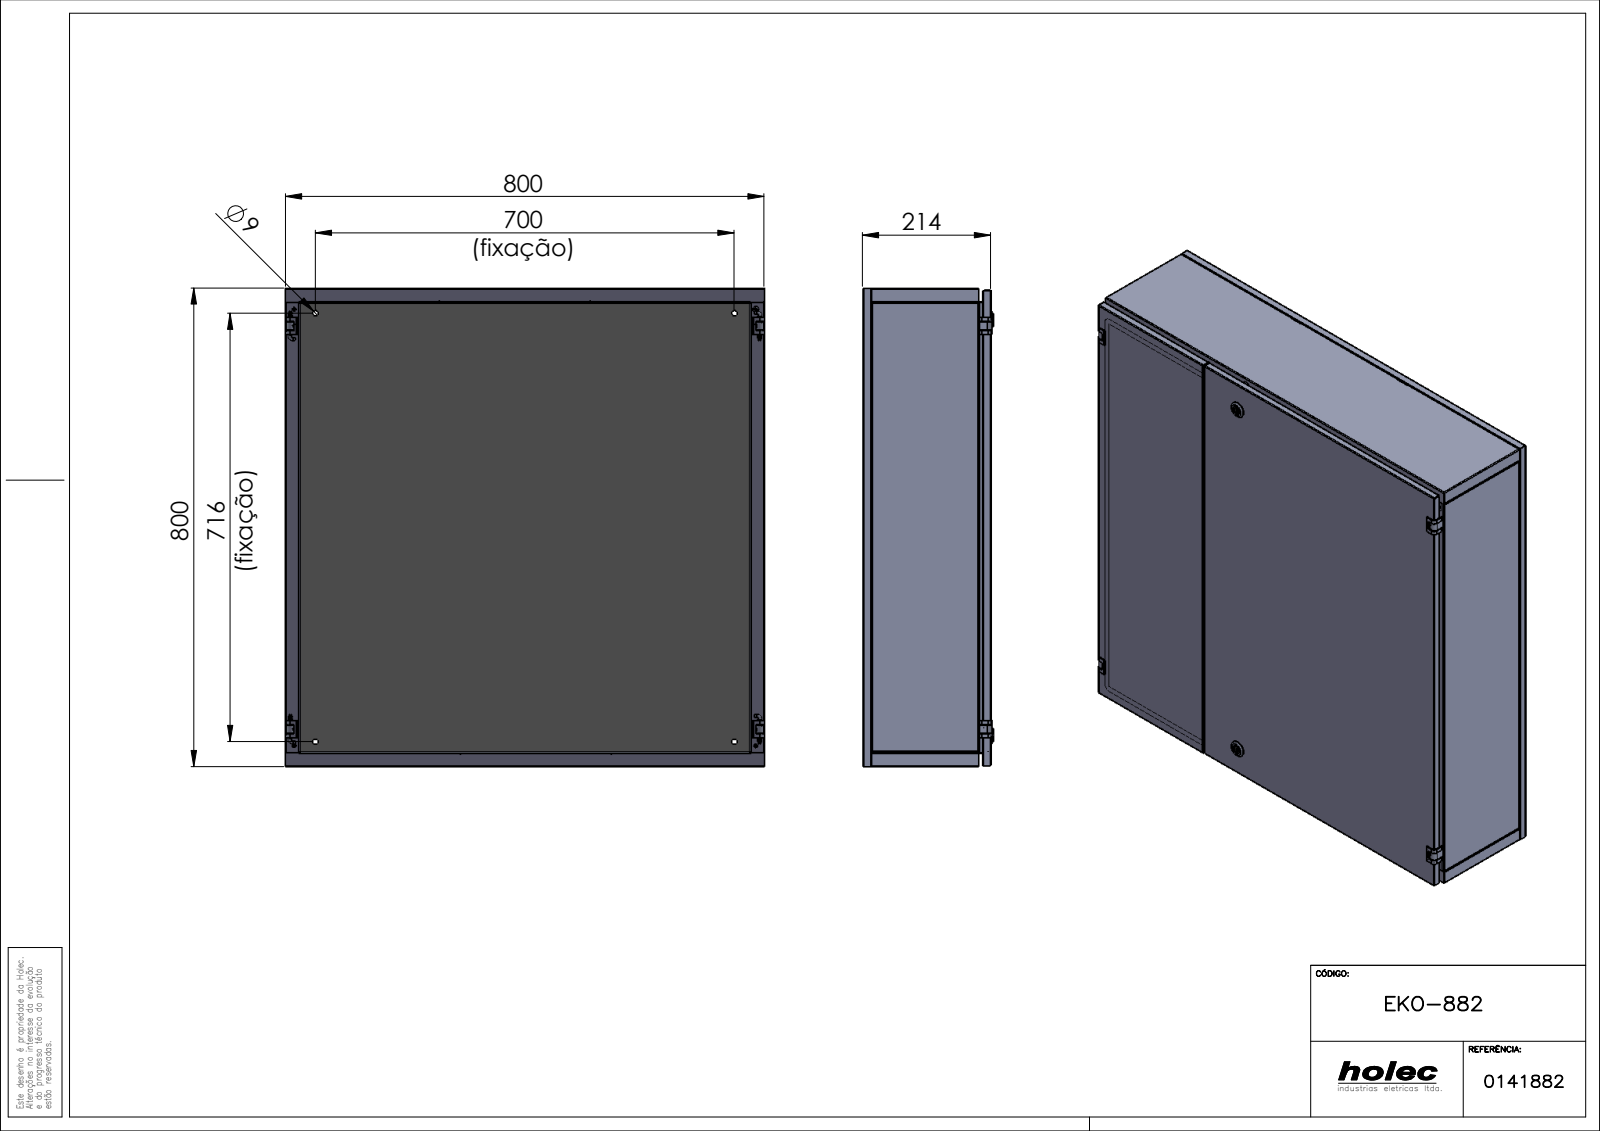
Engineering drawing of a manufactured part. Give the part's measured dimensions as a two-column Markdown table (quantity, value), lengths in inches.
| quantity | value |
| --- | --- |
| part name | EKO-882 |
| STEP written by | SolidWorks 2017 (AUTOMOTIVE_DESIGN) |
| units | inches |
| bodies | 53 solids, 3633 faces (1785 planar, 1142 cylindrical, 706 other) |
| overall size | 31.496 × 31.496 × 8.587 |
| volume | 153.6 in³ |
| surface area | 7 572 in² |
| round holes (diameter × count) | 0.169 × 36, 0.236 × 14, 0.165 × 12, 0.217 × 8, 0.433 × 8, 0.197 × 6, 0.13 × 4, 0.157 × 4, 0.354 × 4, 0.161 × 2, 0.394 × 2, 0.398 × 2 |
| round bosses / shafts (diameter × count) | 0.157 × 4, 1.102 × 2, 0.748 × 2, 0.618 × 2, 0.591 × 2, 0.5 × 2, 0.374 × 2, 0.23 × 2 |
| partial cylindrical surfaces (radius × count) | 0.008 × 152, 0.059 × 59, 0.02 × 57, 0.012 × 40, 0.039 × 22, 0.098 × 14, 0.079 × 8, 0.177 × 6 |
| main face-to-face distances | 0.039, 8.39, 8.35, 8.429, 31.457, 31.417, 31.496, 0.945, 30.512, 0.902 |
| hole center spacings | 0.984, 1.236, 9.97, 9.921, 1.969, 2.106, 10.115, 0.748 |
